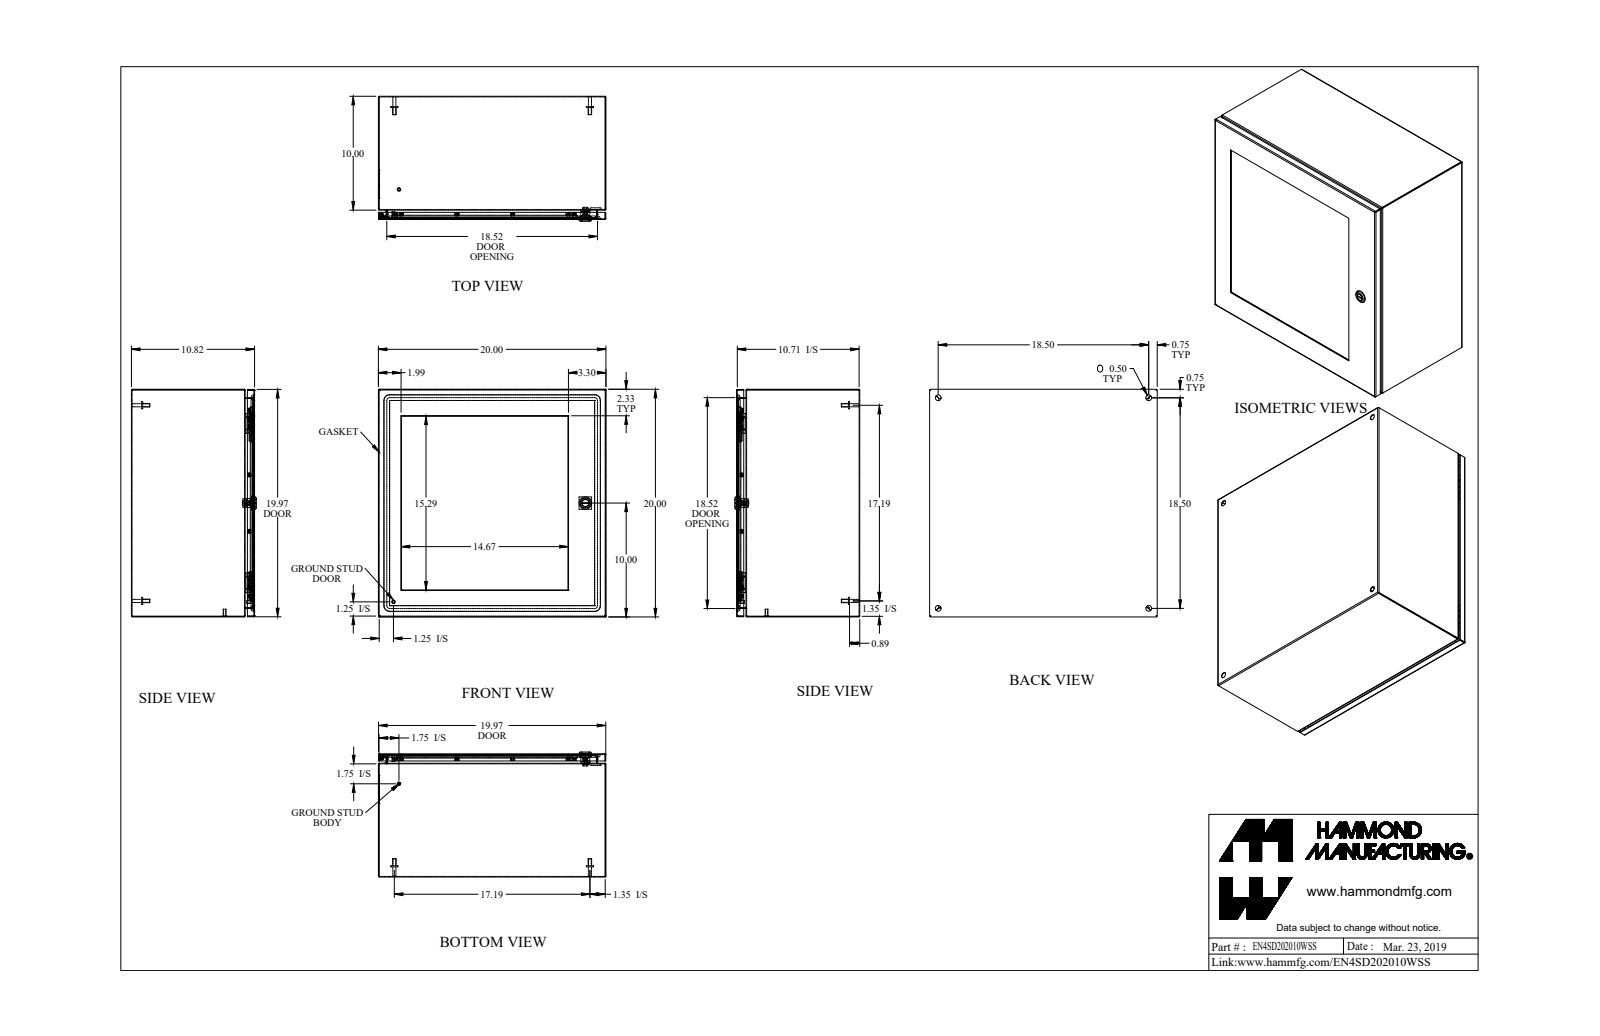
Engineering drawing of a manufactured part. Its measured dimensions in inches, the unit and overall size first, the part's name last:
Units: inches
Overall size (bounding box): 20 × 20 × 10.982
Round holes (diameter × count): ⌀0.13 ×16, ⌀0.25 ×16, ⌀0.5 ×5, ⌀0.172 ×1, ⌀0.197 ×1, ⌀0.24 ×1, ⌀0.242 ×1, ⌀0.387 ×1, ⌀0.63 ×1, ⌀0.768 ×1
Round bosses / shafts (diameter × count): ⌀0.226 ×17, ⌀0.368 ×16, ⌀0.164 ×16, ⌀0.313 ×6, ⌀0.625 ×4, ⌀0.275 ×4, ⌀0.25 ×2, ⌀1.1 ×1
Partial cylindrical surfaces — rounded edges, fillets, slot ends (radius × count): R0.029 ×21, R0.086 ×21, R0.188 ×12, R0.125 ×10, R0.006 ×4, R0.016 ×4, R0.062 ×4, R0.088 ×4
Main face-to-face distances: 0.057, 19.943, 10.765, 19.886, 10.708, 20, 0.25, 10.458, 10.515, 0.307
Hole centre spacings: 9.78, 16.333, 4.889, 4.89, 4.89, 4.891, 10.324, 16.471
Volume: 161 in³ · Surface area: 3 941 in²
Bodies: 63 solids, 1287 faces (646 planar, 387 cylindrical, 254 other)
Part name (STEP PRODUCT): EN4SD202010WSS_Default
STEP written by: SolidWorks 2019 (CONFIG_CONTROL_DESIGN)
